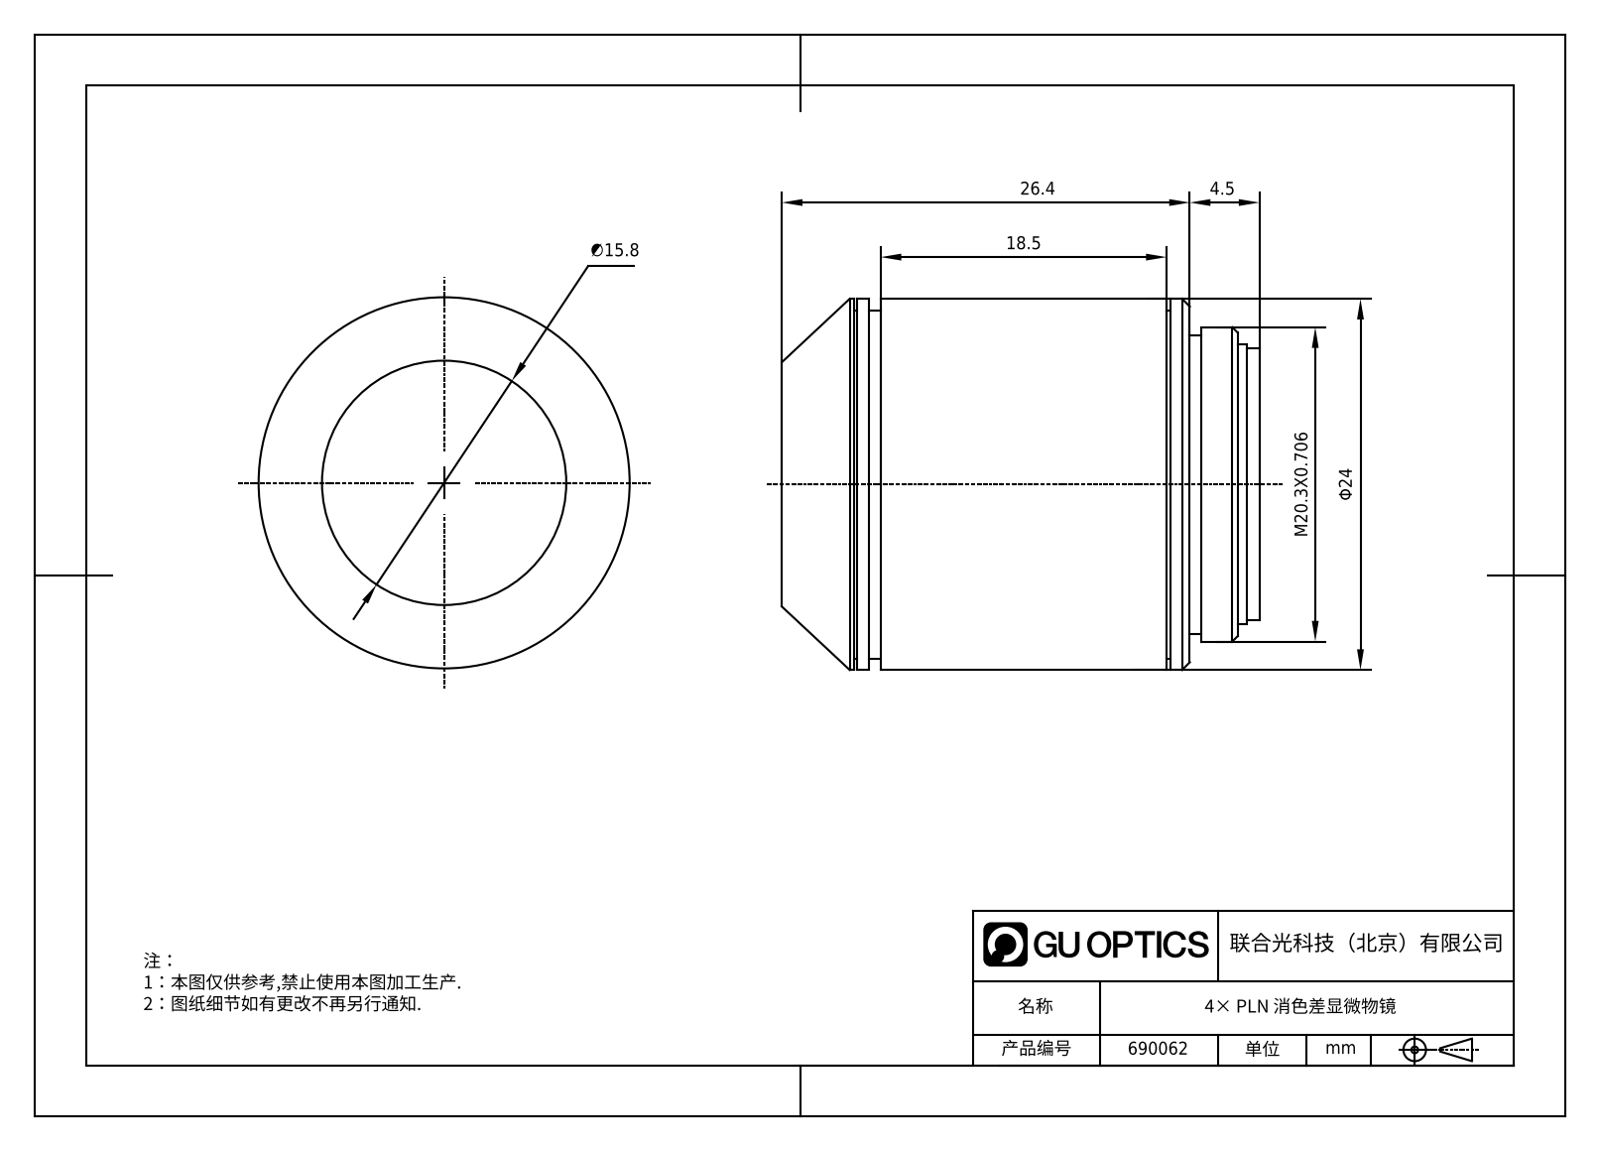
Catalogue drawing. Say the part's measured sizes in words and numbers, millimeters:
The part is named "690062". Its 3-D file was written by "SolidWorks 2020 (CONFIG_CONTROL_DESIGN)". It is 1 solid with 40 faces: 12 planar, 22 cylindrical and 6 other. Overall it measures 30.89 by 24 by 24 millimeters. Its volume is 12 587 cubic millimeters and its surface area 3 306 square millimeters. Round bosses or shafts: 1 of diameter 24, 1 of diameter 22.5, 1 of diameter 20.32, 1 of diameter 19.32, 1 of diameter 18.12, 1 of diameter 17.62. The main face-to-face distances are 30.89, 0.75, 26.39, 4.5, 20.25, 1.5, 20, 20.75, 21.5, 4.64.
